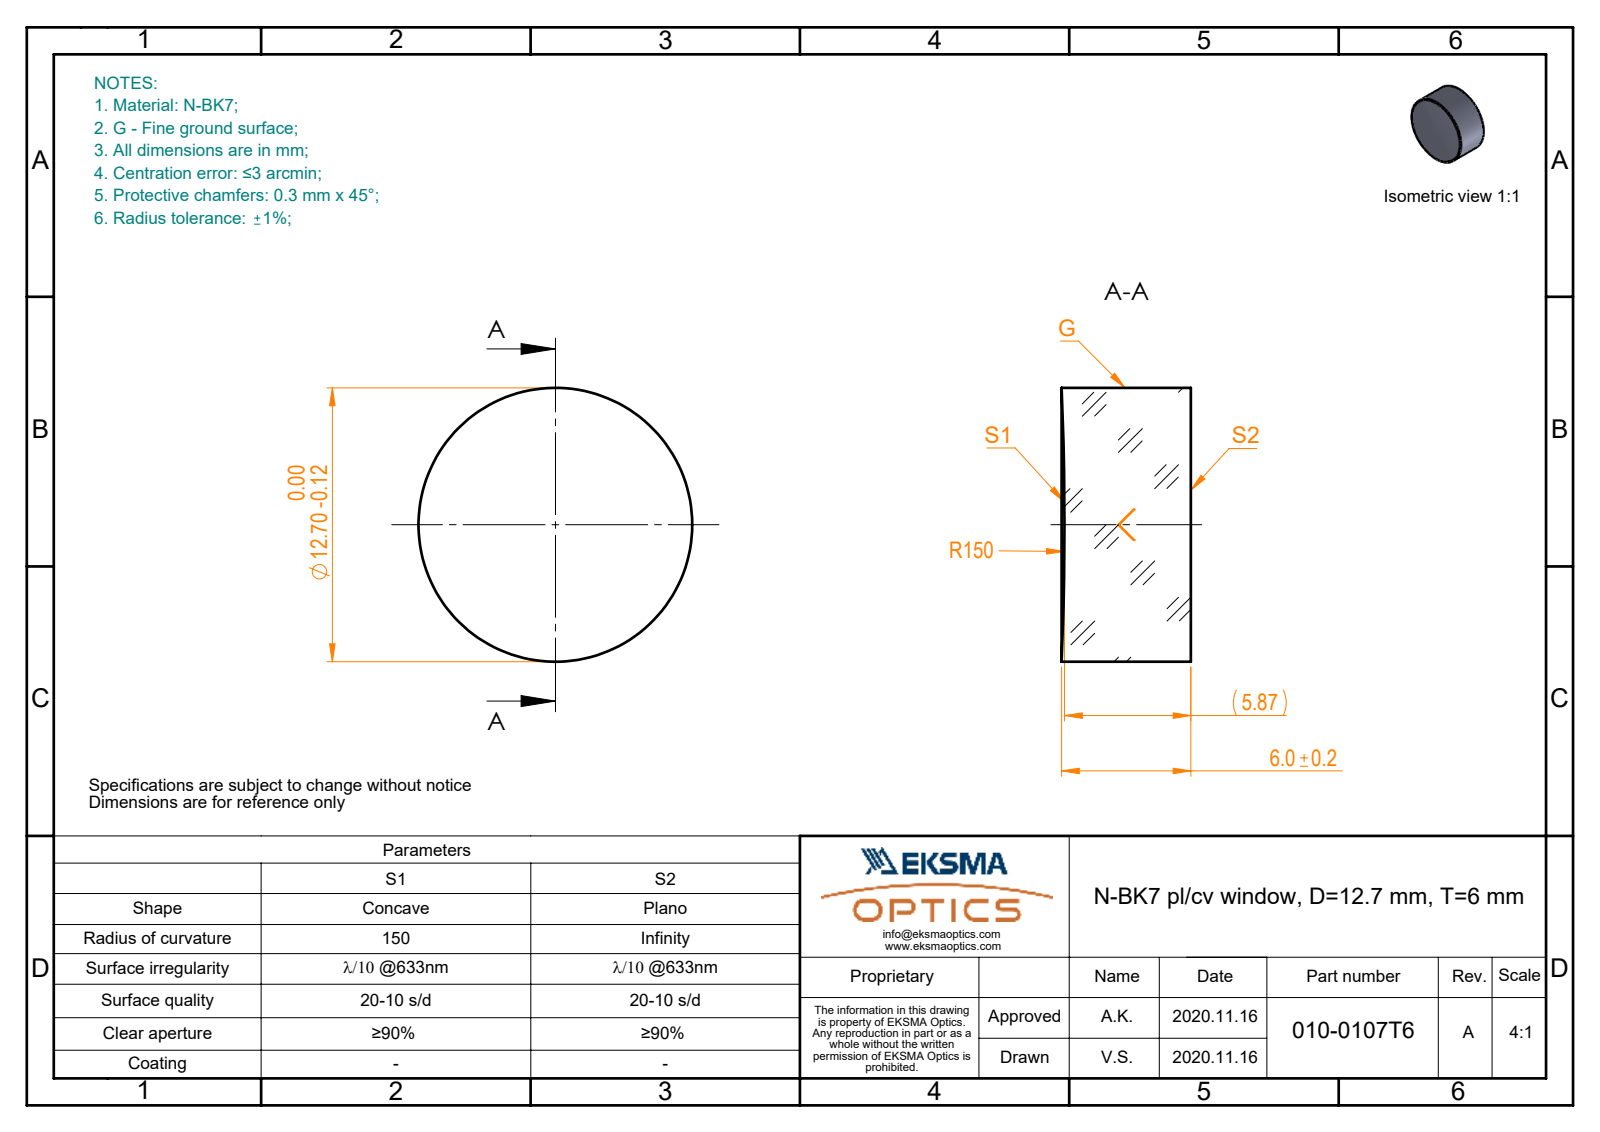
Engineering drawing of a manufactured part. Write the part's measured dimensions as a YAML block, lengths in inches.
part_name: "010-0107T6_N-BK7_PCV_window"
step_written_by: "SolidWorks 2019 (CONFIG_CONTROL_DESIGN)"
units: inches
bodies: {solids: 1, faces: 5, planar: 1, cylindrical: 2, other: 2}
overall_size: [0.5, 0.5, 0.236]
volume: 0.046
surface_area: 0.764
round_bosses_or_shafts:
  - {diameter: 0.5, count: 1}
